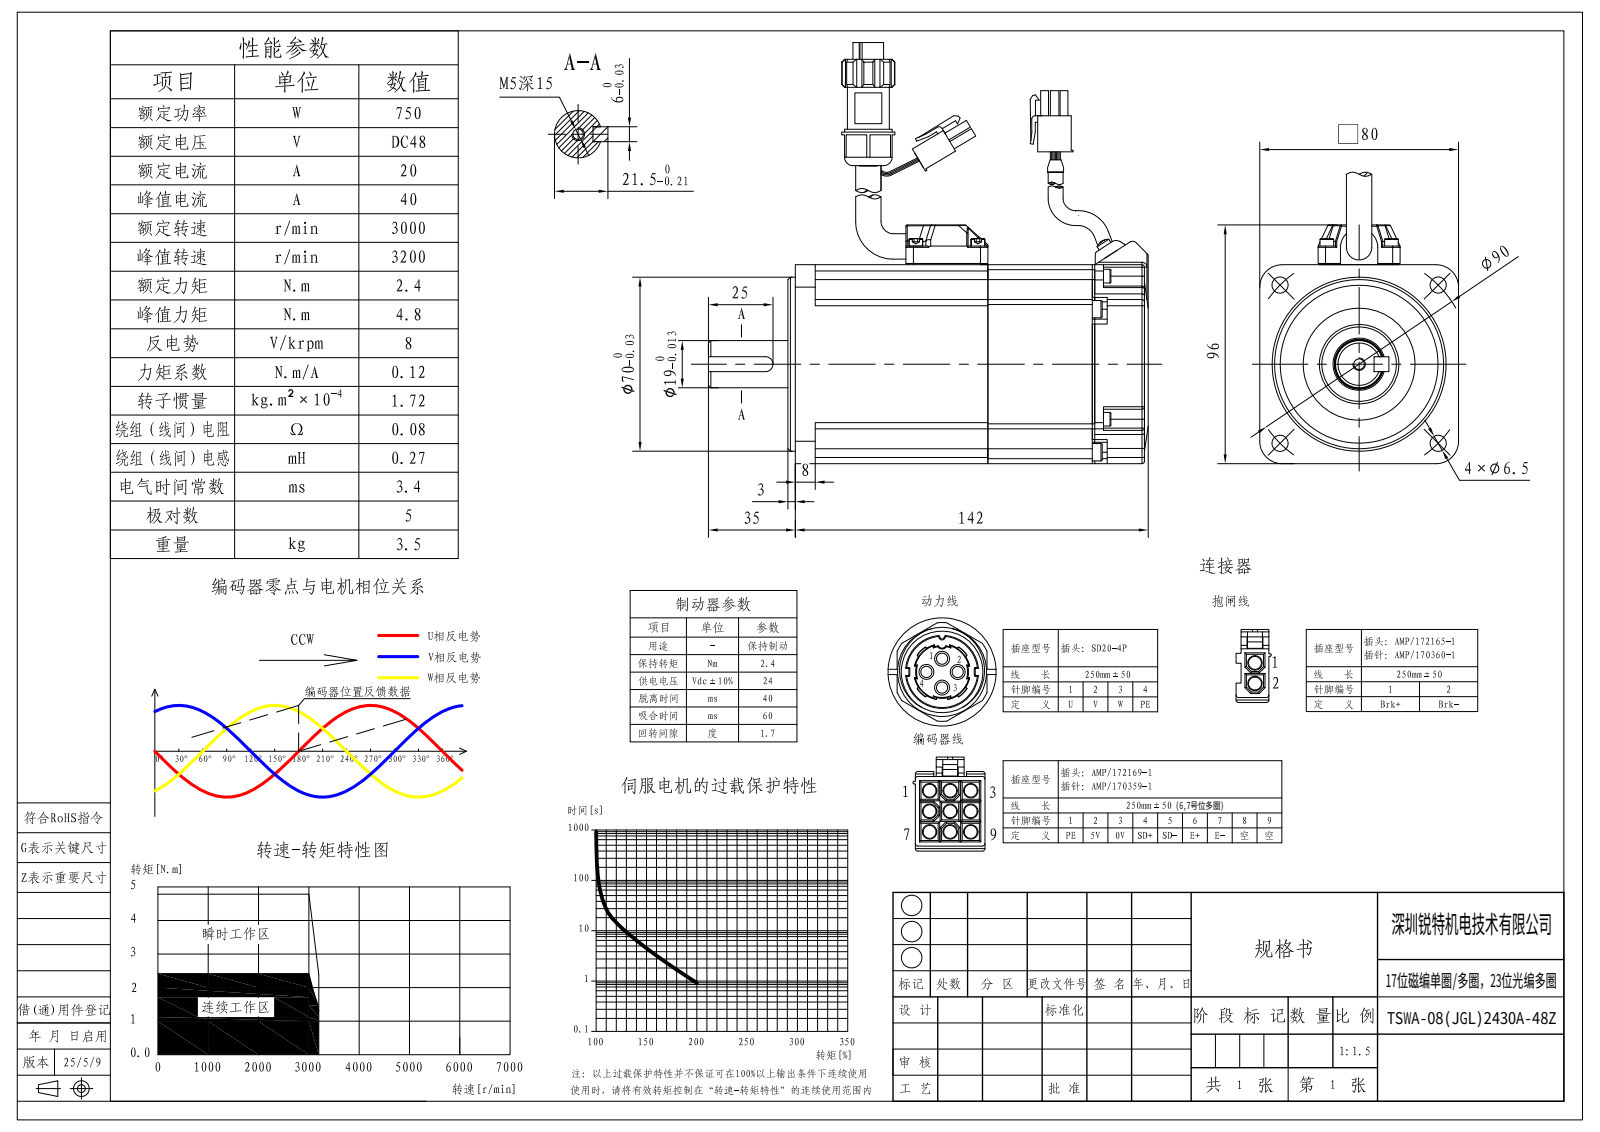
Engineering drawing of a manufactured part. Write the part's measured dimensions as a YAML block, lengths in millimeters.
step_written_by: "SolidWorks 2018 (CONFIG_CONTROL_DESIGN)"
units: millimeters
bodies: {solids: 7, faces: 843, planar: 362, cylindrical: 349, other: 132}
overall_size: [177, 93.5, 80]
volume: 813649
surface_area: 90174
round_holes:
  - {diameter: 3.3, count: 10}
  - {diameter: 2.5, count: 5}
  - {diameter: 4.2, count: 5}
  - {diameter: 2, count: 4}
  - {diameter: 3.5, count: 4}
  - {diameter: 6.5, count: 4}
  - {diameter: 6, count: 1}
  - {diameter: 6.3, count: 1}
  - {diameter: 7.6, count: 1}
  - {diameter: 8, count: 1}
  - {diameter: 10, count: 1}
  - {diameter: 11.8, count: 1}
round_bosses_or_shafts:
  - {diameter: 4, count: 6}
  - {diameter: 7, count: 4}
  - {diameter: 5.5, count: 4}
  - {diameter: 3, count: 4}
  - {diameter: 2.2, count: 2}
  - {diameter: 70, count: 1}
  - {diameter: 62, count: 1}
  - {diameter: 45, count: 1}
partial_cylinders:
  - {radius: 1, count: 37}
  - {radius: 2, count: 29}
  - {radius: 0.5, count: 13}
  - {radius: 8, count: 12}
  - {radius: 0.6, count: 9}
  - {radius: 2.5, count: 8}
  - {radius: 4, count: 8}
  - {radius: 3, count: 5}
face_to_face_distances: [80, 14, 138.5, 3, 66, 77.5, 61, 1, 142, 3.5]
hole_center_spacings: [8, 59.04, 86.19, 10.33, 10.34, 16, 18.78, 41.75]
